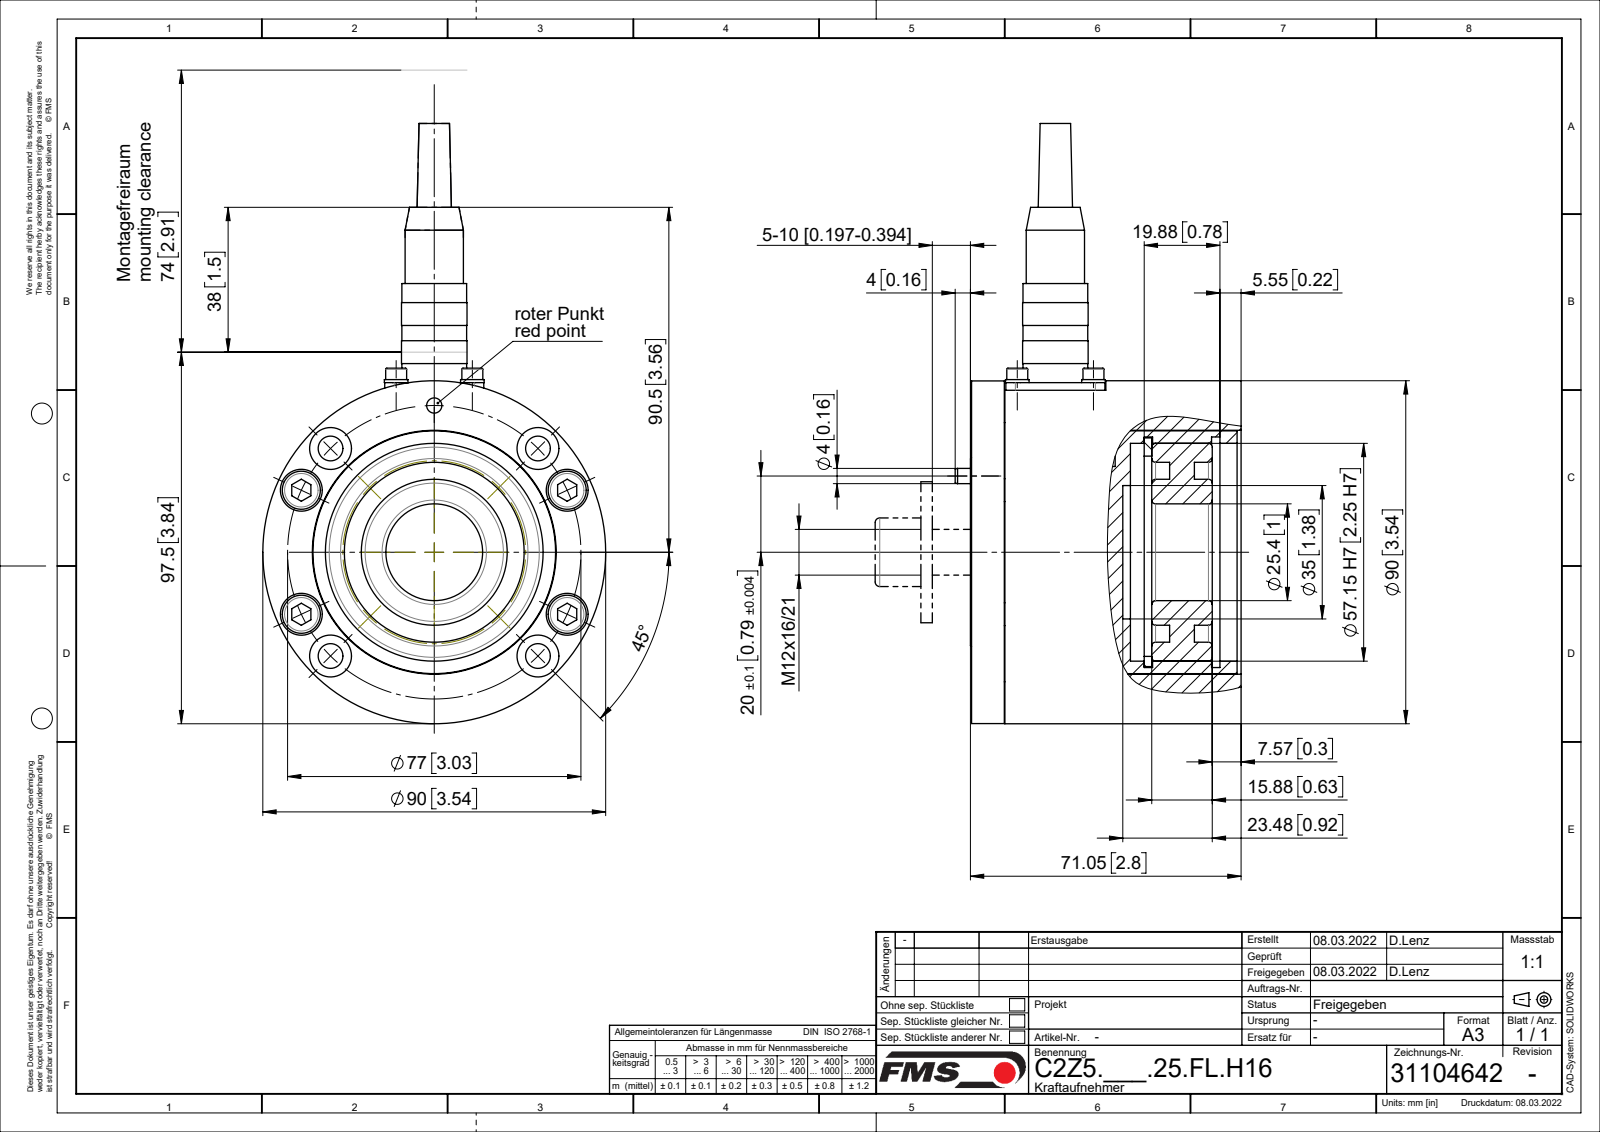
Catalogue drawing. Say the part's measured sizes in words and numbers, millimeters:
The part is named "31104496_stp_01; Federringe_DIN127A_M03; Flanschstecker_M14x1_Mini_5pol; Sch DIN9021_M12 (+8 more)". Its 3-D file was written by "SolidWorks 2018 (CONFIG_CONTROL_DESIGN)". It is 22 solids with 547 faces: 185 planar, 254 cylindrical and 108 other. Overall it measures 157.5 by 96.05 by 90 millimeters. Its volume is 316 332 cubic millimeters and its surface area 122 946 square millimeters. Round holes: 8 of diameter 6.5, 8 of diameter 11, 6 of diameter 2.5, 4 of diameter 3.1, 4 of diameter 3.2, 4 of diameter 5, 4 of diameter 7, 2 of diameter 4, 1 of diameter 3, 1 of diameter 10.2, 1 of diameter 12, 1 of diameter 13. Round bosses or shafts: 5 of diameter 1.5, 4 of diameter 10, 4 of diameter 6.2, 4 of diameter 6, 4 of diameter 5.5, 4 of diameter 3, 1 of diameter 90, 1 of diameter 89.9. Partial cylindrical surfaces (rounded edges, fillets, slot ends): 4 of radius 0.1, 4 of radius 2.5, 2 of radius 0.5, 2 of radius 4.16, 2 of radius 5, 1 of radius 23.2, 1 of radius 26.29. The main face-to-face distances are 6, 33.05, 32, 2, 38, 8.6, 29.1, 37.7, 2.9, 5.7. The hole center spacings are 20, 38.5, 13.37, 14.14, 38.49, 44.16, 54.44, 63.07.
